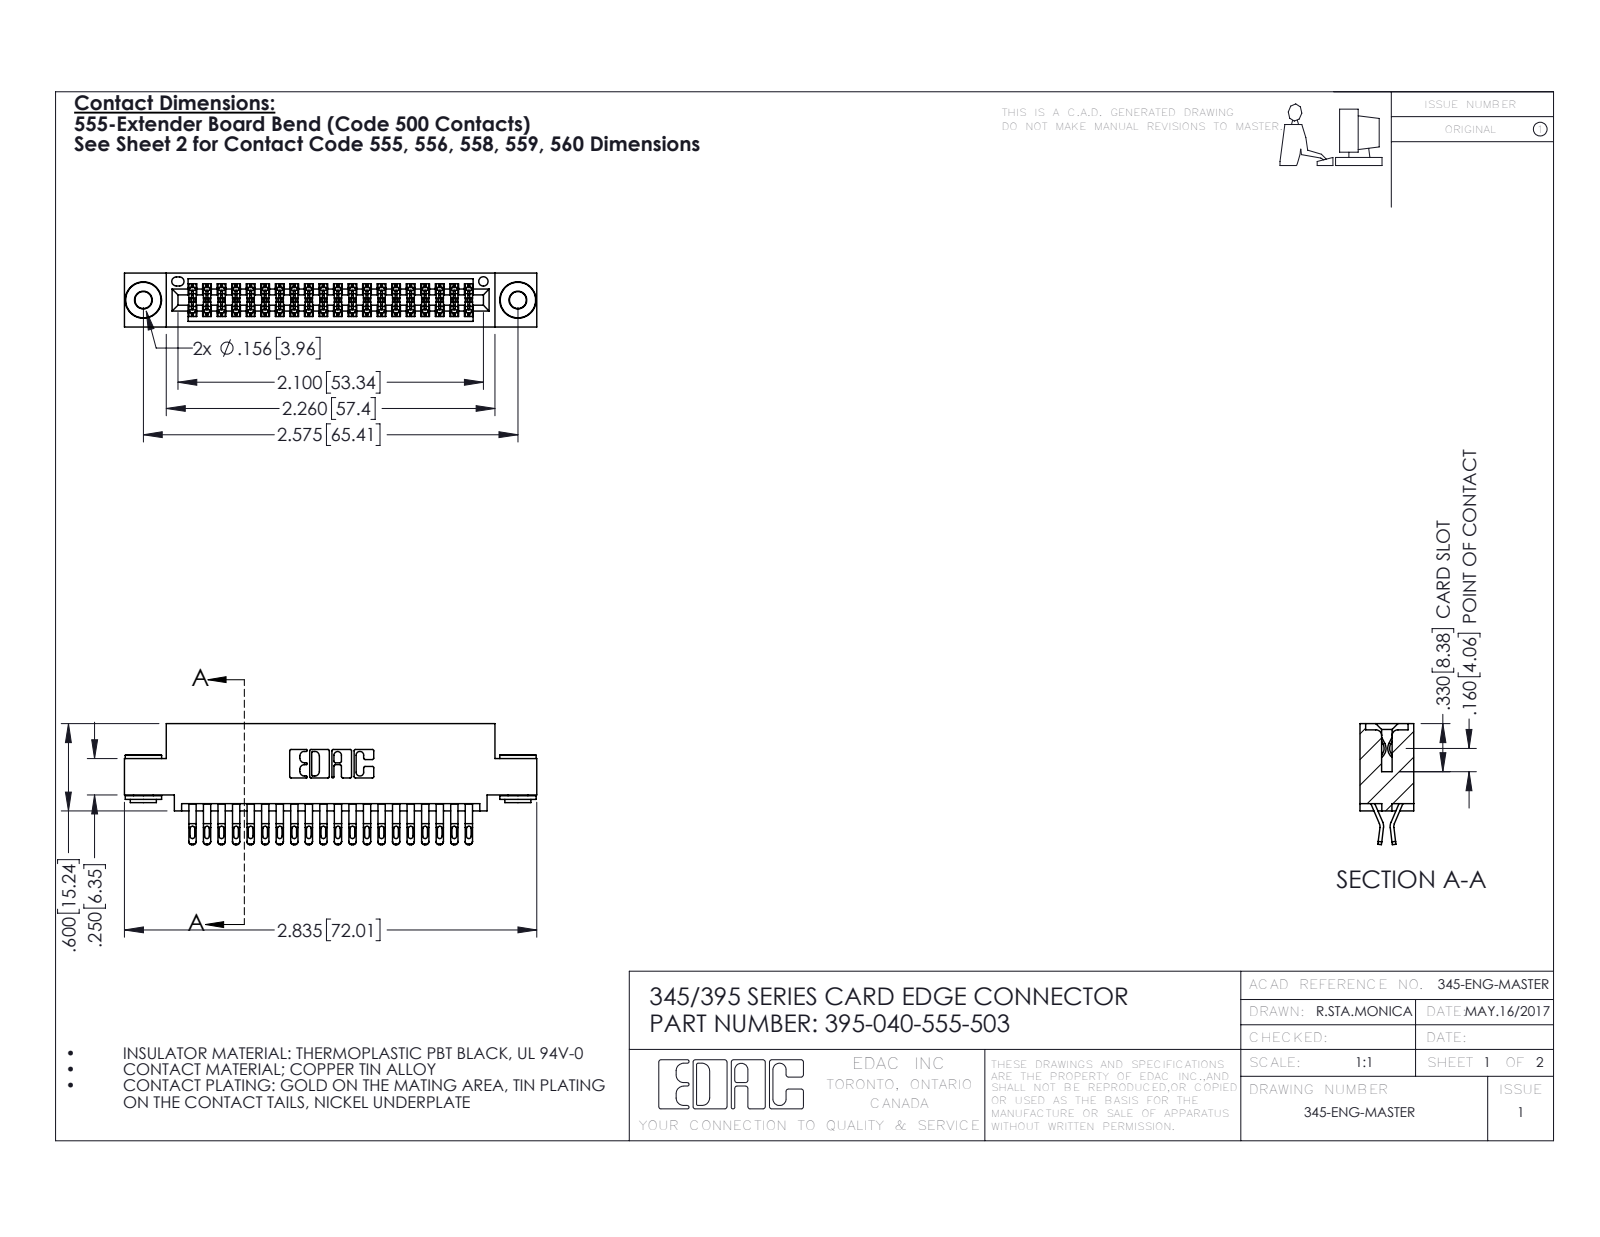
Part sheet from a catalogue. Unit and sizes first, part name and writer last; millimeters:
Units: millimetres
Overall size (bounding box): 72 × 21.1 × 9.4
Round holes (diameter × count): ⌀2.9 ×2, ⌀4 ×2, ⌀1.6 ×1
Round bosses / shafts (diameter × count): ⌀6.4 ×2, ⌀4.6 ×2, ⌀3.5 ×2
Partial cylindrical surfaces — rounded edges, fillets, slot ends (radius × count): R0.4 ×100, R0.5 ×80, R0.2 ×60, R0.3 ×22, R0.2 ×6, R0.8 ×6, R0.7 ×3, R0.3 ×2
Main face-to-face distances: 1.8, 7.6, 0.6, 5.1, 9.4, 2.5, 6.9, 5.7, 4.4, 3.8
Hole centre spacings: 6.9, 59.5, 65.4
Volume: 6 850 mm³ · Surface area: 10 410 mm²
Bodies: 43 solids, 2408 faces (1334 planar, 1066 cylindrical, 8 other)
Part name (STEP PRODUCT): 345-250-002_345-250-002-102; 345 Part_0.110 Offset - 0.156 Dia-TH; 345-292-001_555 Tail; 395-040-555-503
STEP written by: SolidWorks 2016 (CONFIG_CONTROL_DESIGN)
